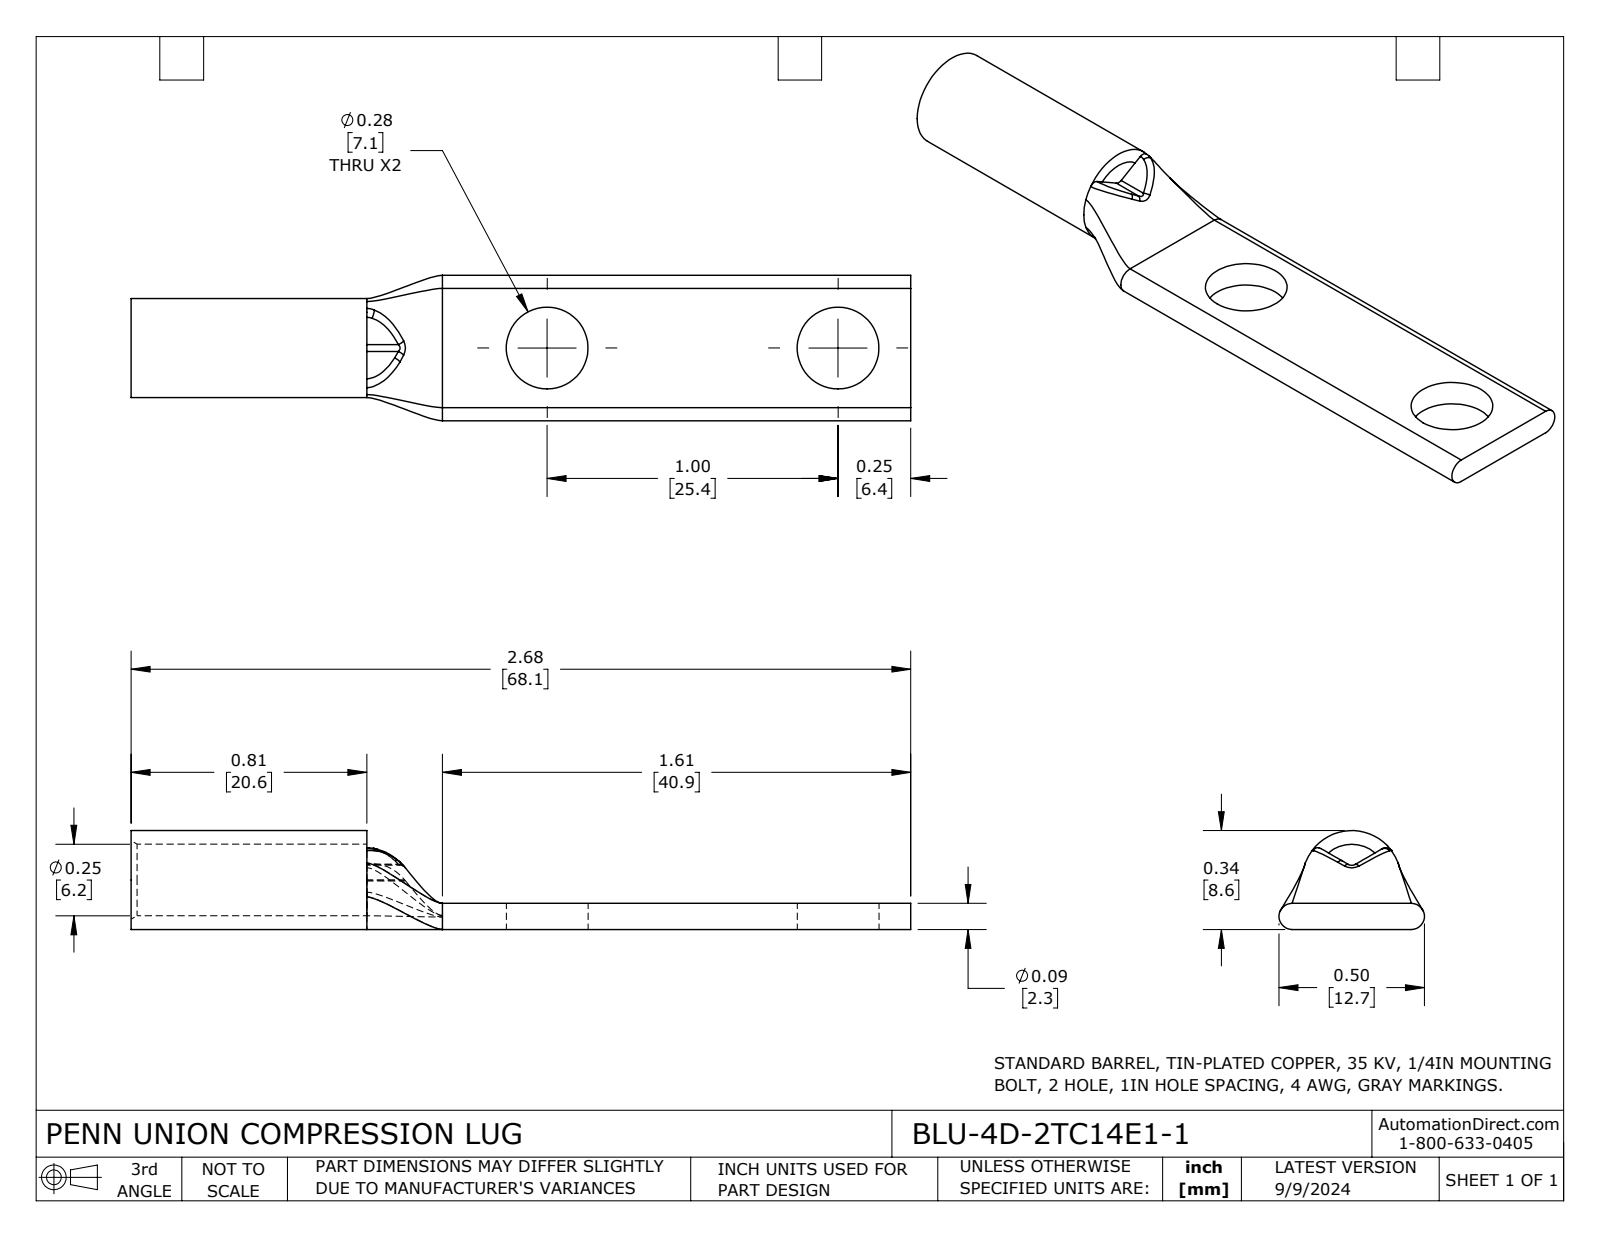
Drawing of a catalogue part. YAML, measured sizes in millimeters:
part_name: "BLU-4D-2TC14E1-1"
step_written_by: "SolidWorks 2023 (CONFIG_CONTROL_DESIGN)"
units: millimeters
bodies: {solids: 1, faces: 39, planar: 11, cylindrical: 13, other: 15}
overall_size: [68.1, 12.7, 8.6]
volume: 1700
surface_area: 2455
round_holes:
  - {diameter: 7.1, count: 2}
  - {diameter: 6.2, count: 1}
round_bosses_or_shafts:
  - {diameter: 8.6, count: 1}
partial_cylinders:
  - {radius: 0.6, count: 2}
  - {radius: 1.1, count: 2}
face_to_face_distances: [2.3, 68.1, 20.6, 47.5, 1.2, 27.2, 6.6, 40.9]
hole_center_spacings: [25.4]
